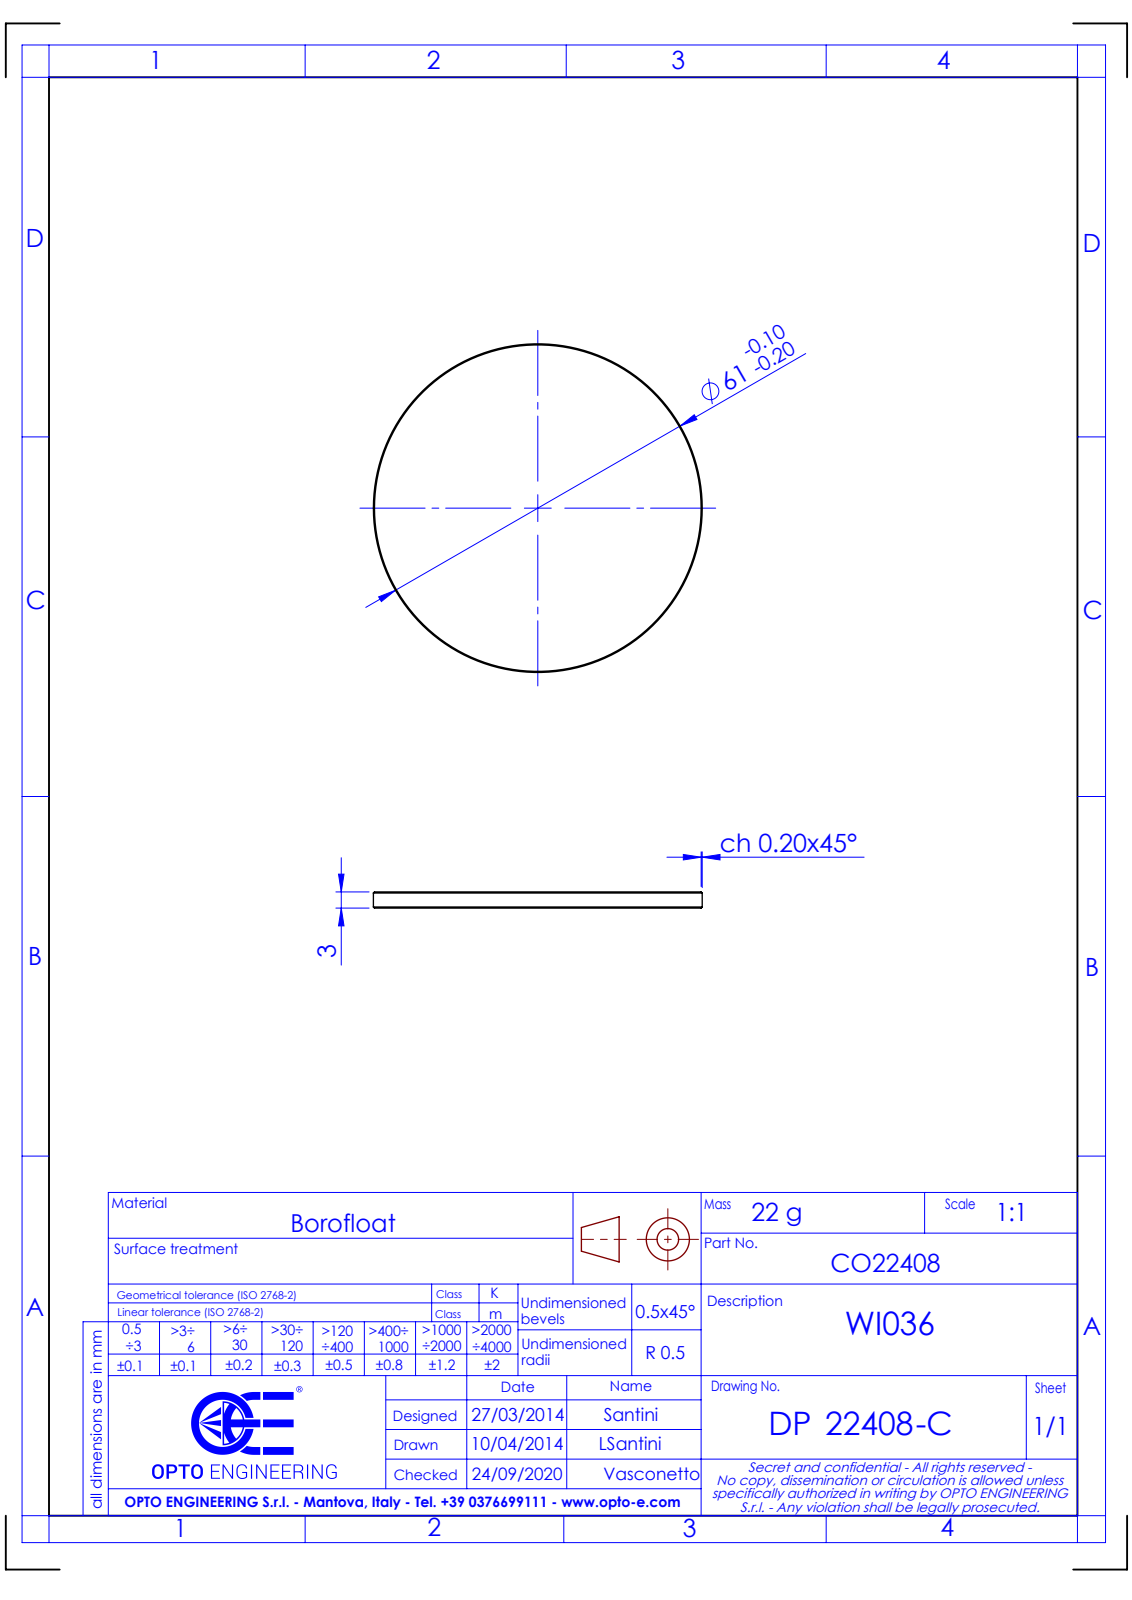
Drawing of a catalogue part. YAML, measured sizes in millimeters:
part_name: "DP22408_WI036"
step_written_by: "SolidWorks 2021 (CONFIG_CONTROL_DESIGN)"
units: millimeters
bodies: {solids: 1, faces: 8, planar: 2, cylindrical: 2, other: 4}
overall_size: [61, 61, 3]
volume: 8760
surface_area: 6375
round_bosses_or_shafts:
  - {diameter: 61, count: 1}
face_to_face_distances: [3]
